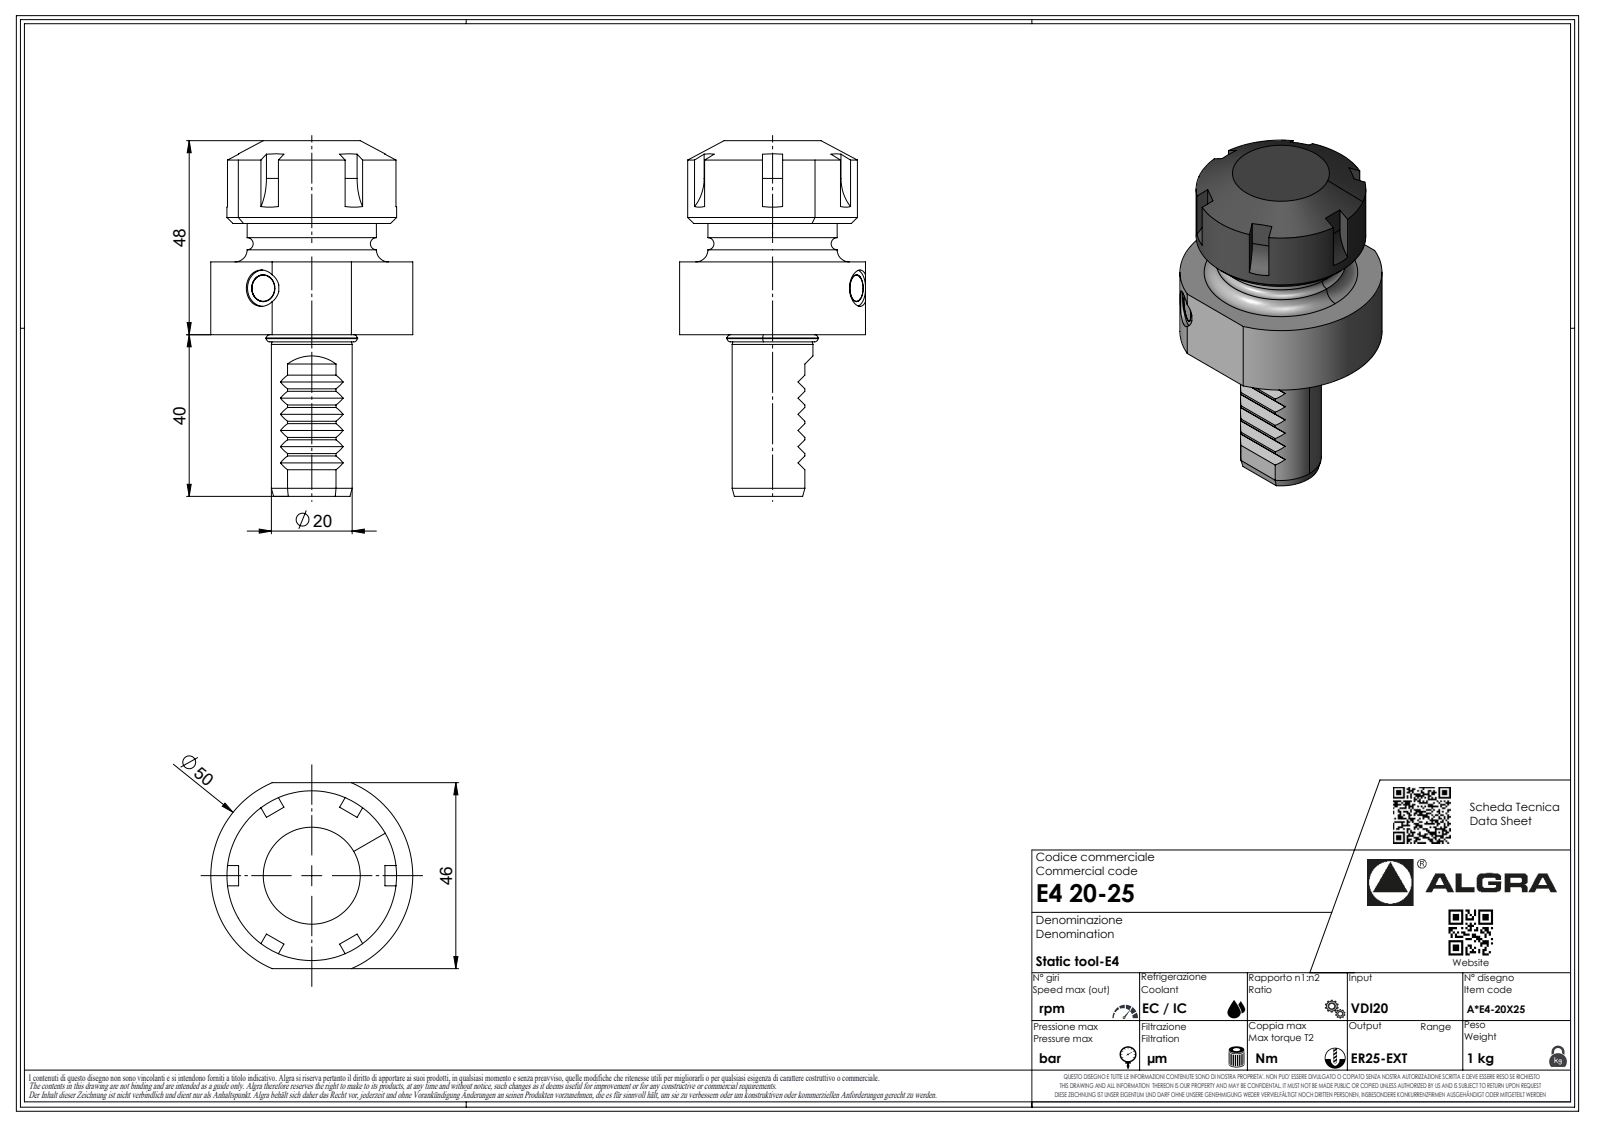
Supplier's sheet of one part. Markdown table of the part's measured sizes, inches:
| quantity | value |
| --- | --- |
| part name | E420-25 |
| STEP written by | SolidWorks 2023 (AUTOMOTIVE_DESIGN) |
| units | inches |
| bodies | 1 solid, 281 faces (194 planar, 41 cylindrical, 46 other) |
| overall size | 3.465 × 1.969 × 1.811 |
| volume | 4.792 in³ |
| surface area | 23.01 in² |
| round holes (diameter × count) | 0.041 × 1, 0.262 × 1, 0.354 × 1 |
| round bosses / shafts (diameter × count) | 1.654 × 1, 1.26 × 1, 0.894 × 1, 0.787 × 1, 0.75 × 1, 0.125 × 1, 0.033 × 1 |
| partial cylindrical surfaces (radius × count) | 0.007 × 7, 0.01 × 7, 0.073 × 7, 0.4 × 6, 0.004 × 1, 0.984 × 1 |
| main face-to-face distances | 0.709, 0.807, 1.181, 1.89, 0.374, 1.083, 1.811, 0.111, 3.465, 2.657 |
